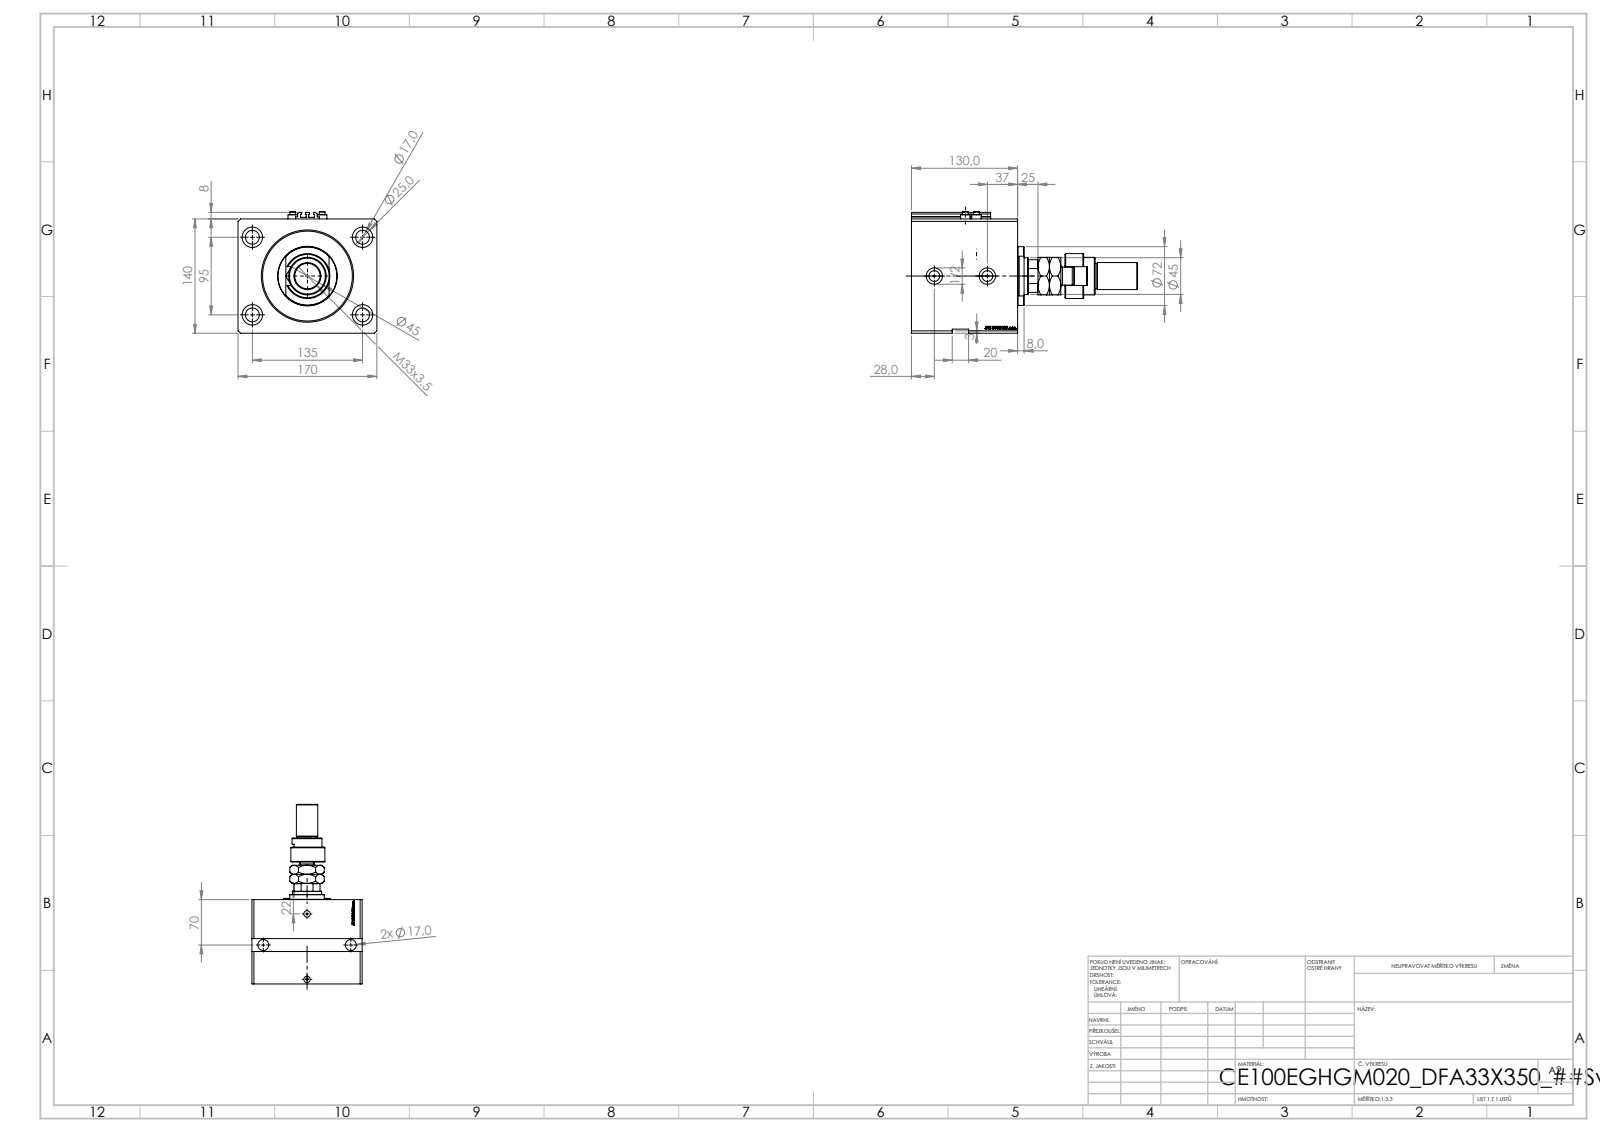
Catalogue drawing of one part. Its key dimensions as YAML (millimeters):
part_name: "FEMALE_PART_FOR_DFA; MFA; V250CE_C_VCP; V250CE_E_Body (+2 more)"
step_written_by: "SolidWorks 2019 (CONFIG_CONTROL_DESIGN)"
units: millimeters
bodies: {solids: 10, faces: 1188, planar: 575, cylindrical: 131, other: 482}
overall_size: [277, 170, 149]
volume: 2941000
surface_area: 323849
round_holes:
  - {diameter: 17, count: 6}
  - {diameter: 1.25, count: 4}
  - {diameter: 4, count: 4}
  - {diameter: 25, count: 4}
  - {diameter: 10, count: 2}
  - {diameter: 13.16, count: 2}
  - {diameter: 20, count: 2}
  - {diameter: 31.5, count: 1}
  - {diameter: 39, count: 1}
  - {diameter: 45, count: 1}
  - {diameter: 100, count: 1}
  - {diameter: 113, count: 1}
round_bosses_or_shafts:
  - {diameter: 11.6, count: 4}
  - {diameter: 7, count: 4}
  - {diameter: 72, count: 1}
  - {diameter: 55, count: 1}
  - {diameter: 46, count: 1}
  - {diameter: 35, count: 1}
  - {diameter: 33, count: 1}
  - {diameter: 31, count: 1}
partial_cylinders:
  - {radius: 0.2, count: 10}
  - {radius: 11.5, count: 1}
  - {radius: 22, count: 1}
face_to_face_distances: [140, 130, 170, 28.9, 101.1, 25, 105, 76.1, 85, 45]
hole_center_spacings: [82.54, 135, 13.6, 33.62, 36, 38.48, 45.69, 49.86]
